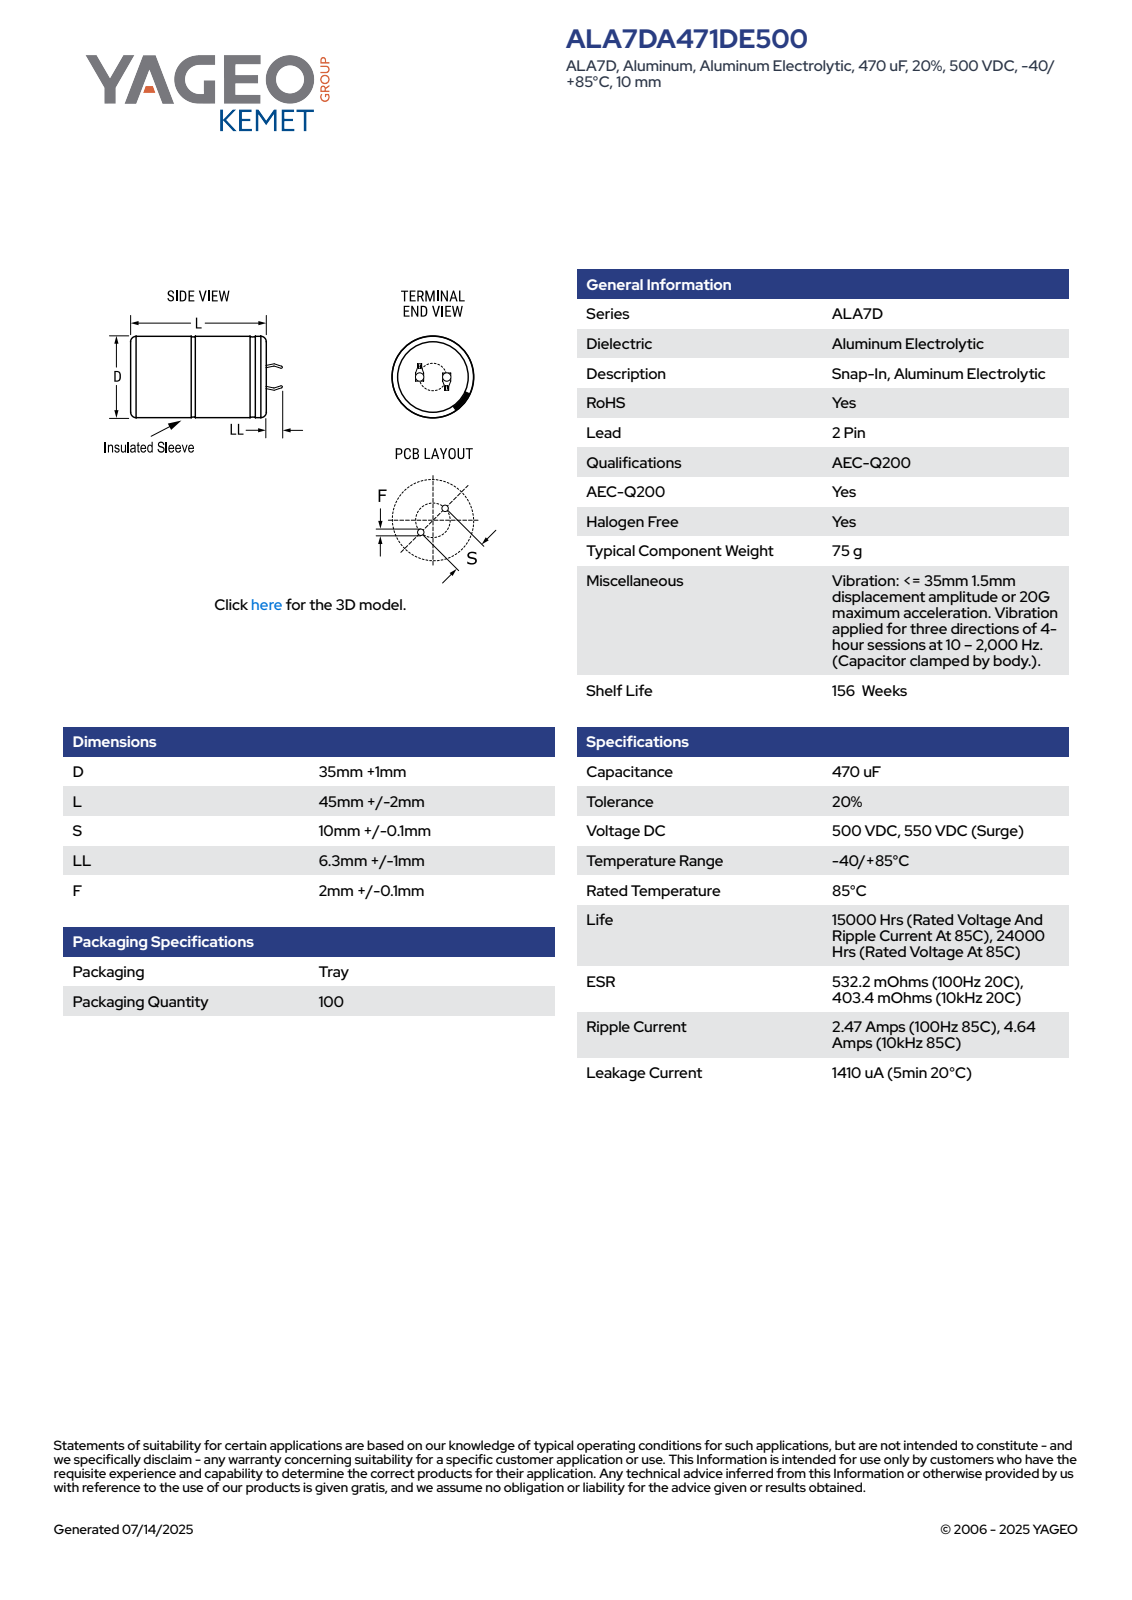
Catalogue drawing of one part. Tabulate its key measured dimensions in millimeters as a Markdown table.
| quantity | value |
| --- | --- |
| part name | CARS_K2PAV_35X45_D36L47S10LL7.3F2.1 |
| STEP written by | SolidWorks 2021 (AUTOMOTIVE_DESIGN) |
| units | millimeters |
| bodies | 1 solid, 106 faces (52 planar, 11 cylindrical, 43 other) |
| overall size | 54.29 × 36 × 36 |
| volume | 47 268 mm³ |
| surface area | 7 410 mm² |
| round holes (diameter × count) | 31.85 × 1 |
| round bosses / shafts (diameter × count) | 36 × 1 |
| partial cylindrical surfaces (radius × count) | 17.99 × 1 |
| main face-to-face distances | 46.99, 0.6, 47.49, 0.5, 7.08, 7.64, 1.35, 0.75, 7.68, 6.48 |
